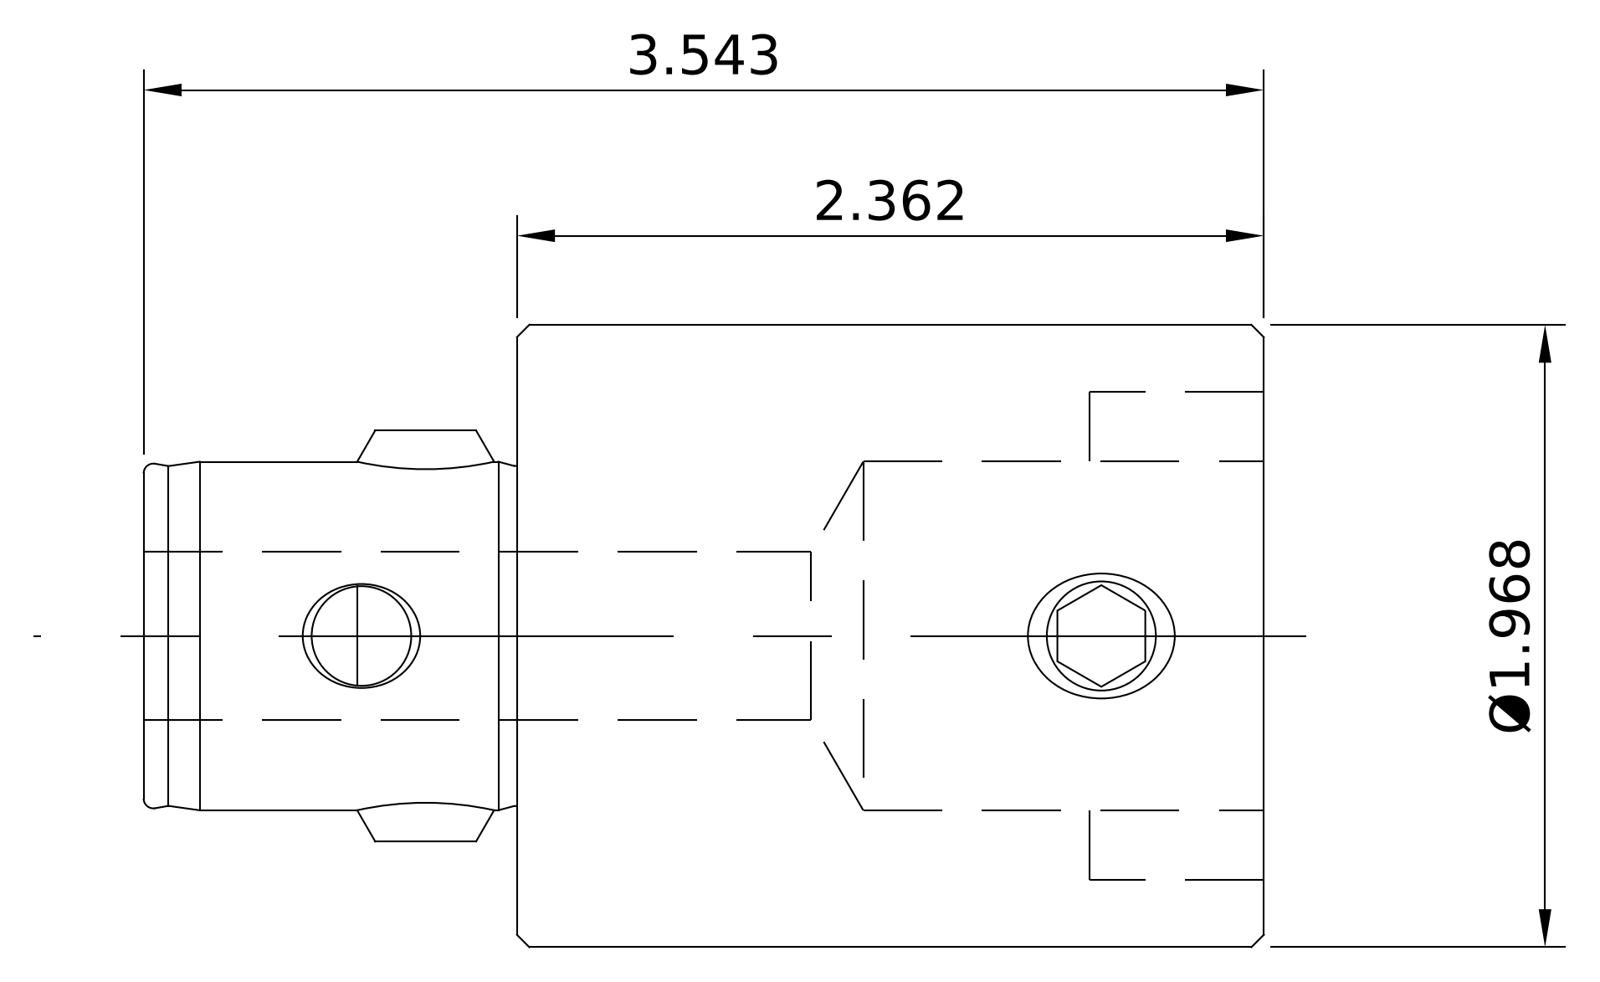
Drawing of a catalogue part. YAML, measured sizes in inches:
part_name: "10.690.43X_10.690.435; 11.331.550; 10.691.50X_10.691.505; 691-50XRing_10.691.505Ring (+1 more)"
step_written_by: "SolidWorks 2016 (AUTOMOTIVE_DESIGN)"
units: inches
bodies: {solids: 4, faces: 132, planar: 37, cylindrical: 43, other: 52}
overall_size: [3.543, 1.969, 1.969]
volume: 6.498
surface_area: 36.64
round_holes:
  - {diameter: 0.177, count: 1}
  - {diameter: 0.315, count: 1}
  - {diameter: 0.335, count: 1}
  - {diameter: 0.406, count: 1}
  - {diameter: 0.433, count: 1}
  - {diameter: 0.531, count: 1}
  - {diameter: 1.102, count: 1}
  - {diameter: 1.122, count: 1}
round_bosses_or_shafts:
  - {diameter: 1.969, count: 1}
  - {diameter: 1.953, count: 1}
  - {diameter: 0.429, count: 1}
  - {diameter: 0.394, count: 1}
  - {diameter: 0.346, count: 1}
  - {diameter: 0.272, count: 1}
partial_cylinders:
  - {radius: 0.177, count: 2}
  - {radius: 0.551, count: 1}
face_to_face_distances: [2.362, 1.181, 3.543, 0.949, 3.008, 1.827, 0.535, 0.157, 0.866, 0.709]
hole_center_spacings: [0.768, 2.341]
